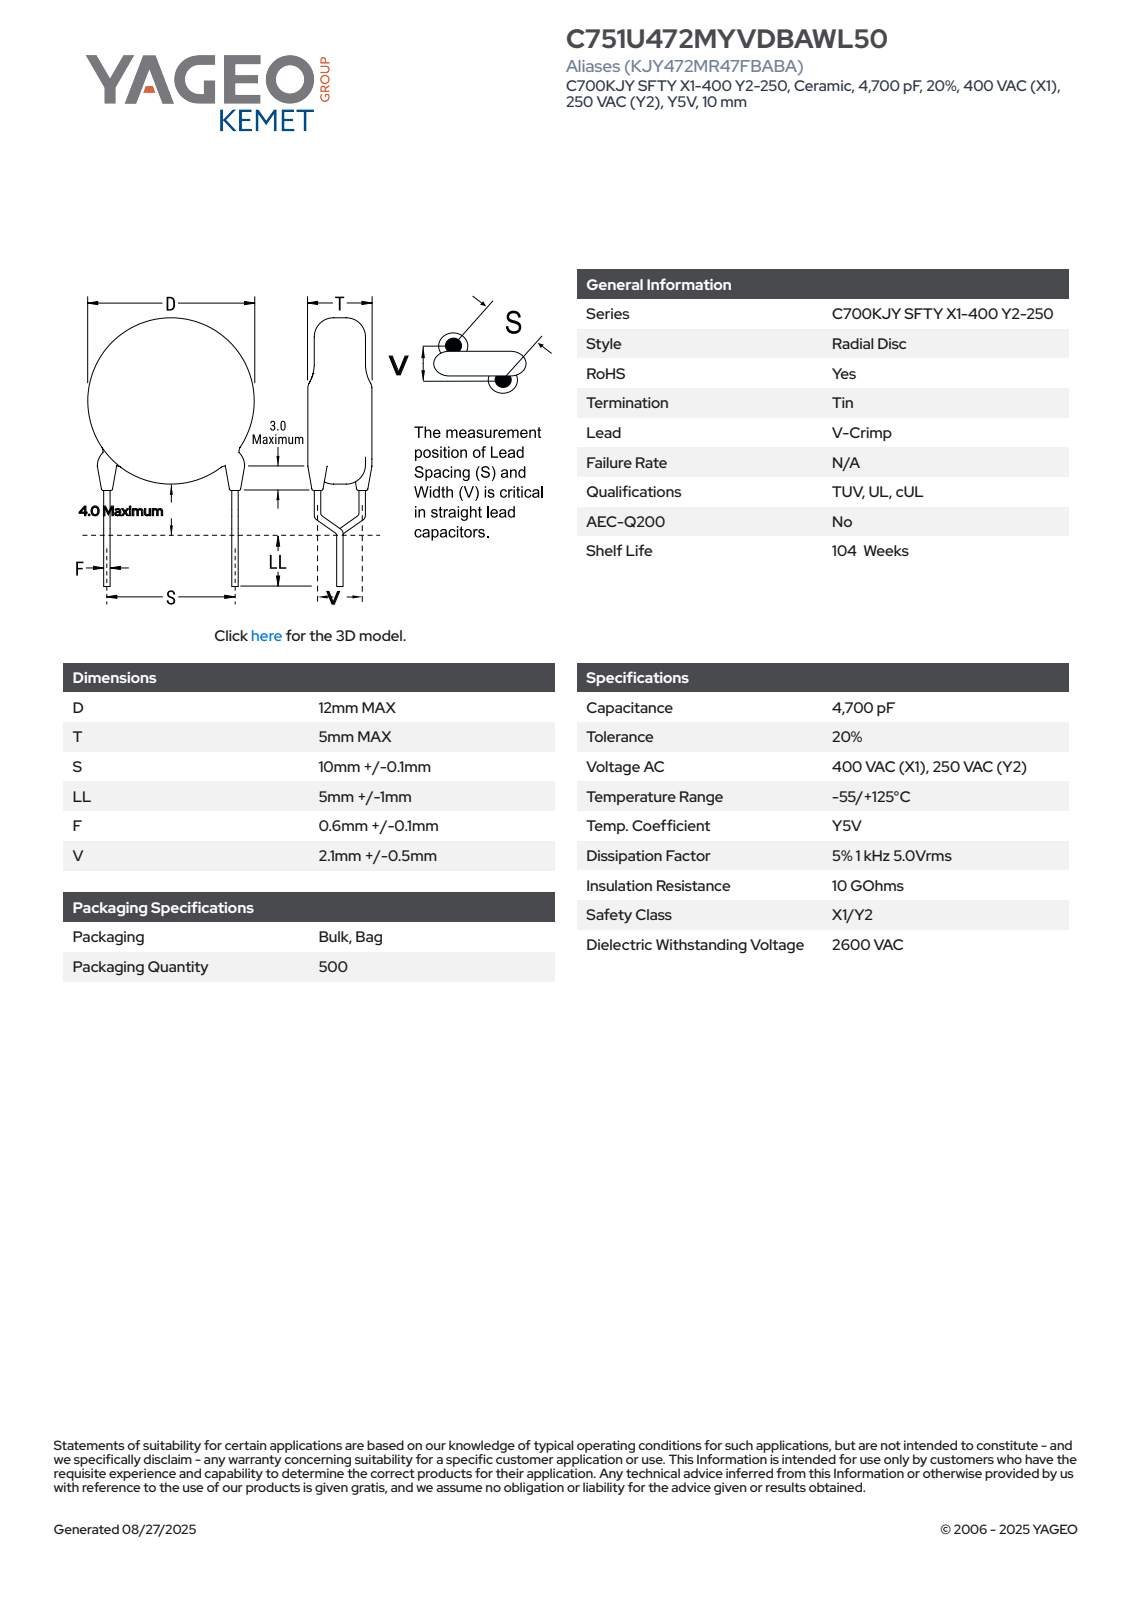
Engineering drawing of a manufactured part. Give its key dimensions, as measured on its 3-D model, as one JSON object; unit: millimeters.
{"part_name": "CCD_VC12X5_D12T5S10LL6F0.7V2.1", "step_written_by": "SolidWorks 2021 (AUTOMOTIVE_DESIGN)", "units": "millimeters", "bodies": {"solids": 4, "faces": 88, "planar": 63, "cylindrical": 21, "other": 4}, "overall_size": [18, 12.16, 5], "volume_mm3": 561, "surface_area_mm2": 452, "round_bosses_or_shafts": [[0.7, 6], [1.2, 2], [12, 1]], "partial_cylinders_radius": [[0.6, 2]], "face_to_face_distances": [5, 6, 13.43, 7.43, 11.5, 5.5, 1.93, 0.53, 0.36, 7.93]}
